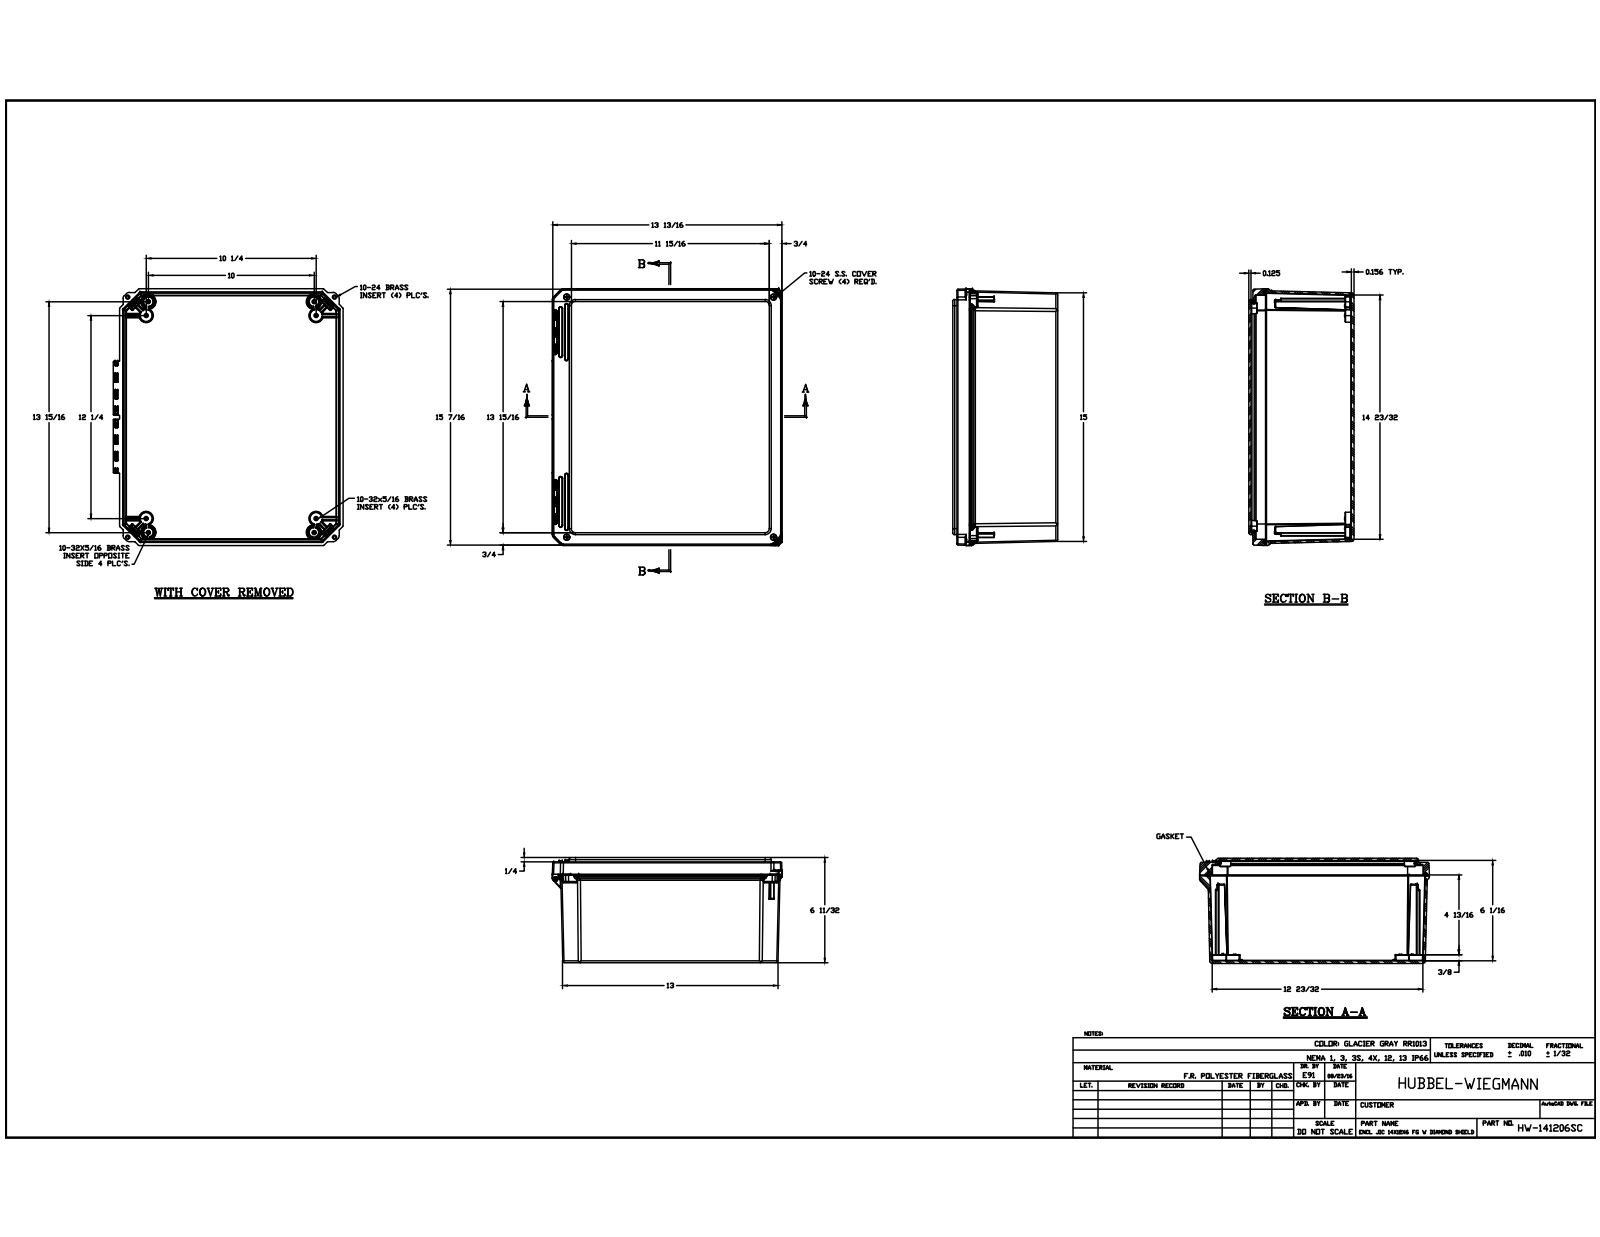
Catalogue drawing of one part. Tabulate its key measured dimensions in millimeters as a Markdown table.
| quantity | value |
| --- | --- |
| part name | HW-141206SC; DS141206BOX; BRASS INSERT-(; BRASS INSERT-(_1 (+5 more) |
| STEP written by | Autodesk Inventor 2017 (CONFIG_CONTROL_DESIGN) |
| units | millimeters |
| bodies | 23 solids, 2149 faces (713 planar, 782 cylindrical, 654 other) |
| overall size | 393.82 × 352.17 × 161.07 |
| volume | 1 978 000 mm³ |
| surface area | 1 034 000 mm² |
| round holes (diameter × count) | 3.96 × 12, 3.86 × 8, 6.4 × 4, 6.43 × 4, 5.56 × 2, 5.77 × 2, 7.94 × 2, 3.48 × 1 |
| round bosses / shafts (diameter × count) | 6.25 × 12, 22.1 × 4, 11.43 × 4, 5.05 × 4, 11.05 × 2 |
| partial cylindrical surfaces (radius × count) | 0.25 × 178, 0.13 × 88, 0.51 × 49, 0.76 × 42, 1.59 × 27, 0.76 × 24, 2.29 × 24, 2.44 × 24 |
| main face-to-face distances | 3.96, 3.17, 157.11, 161.07, 157.9, 153.94, 3.55, 3.53, 6.35, 3.18 |
| hole center spacings | 290.2, 21.35, 32.44, 40.18, 258.06, 285.69, 332.27, 340.76 |
